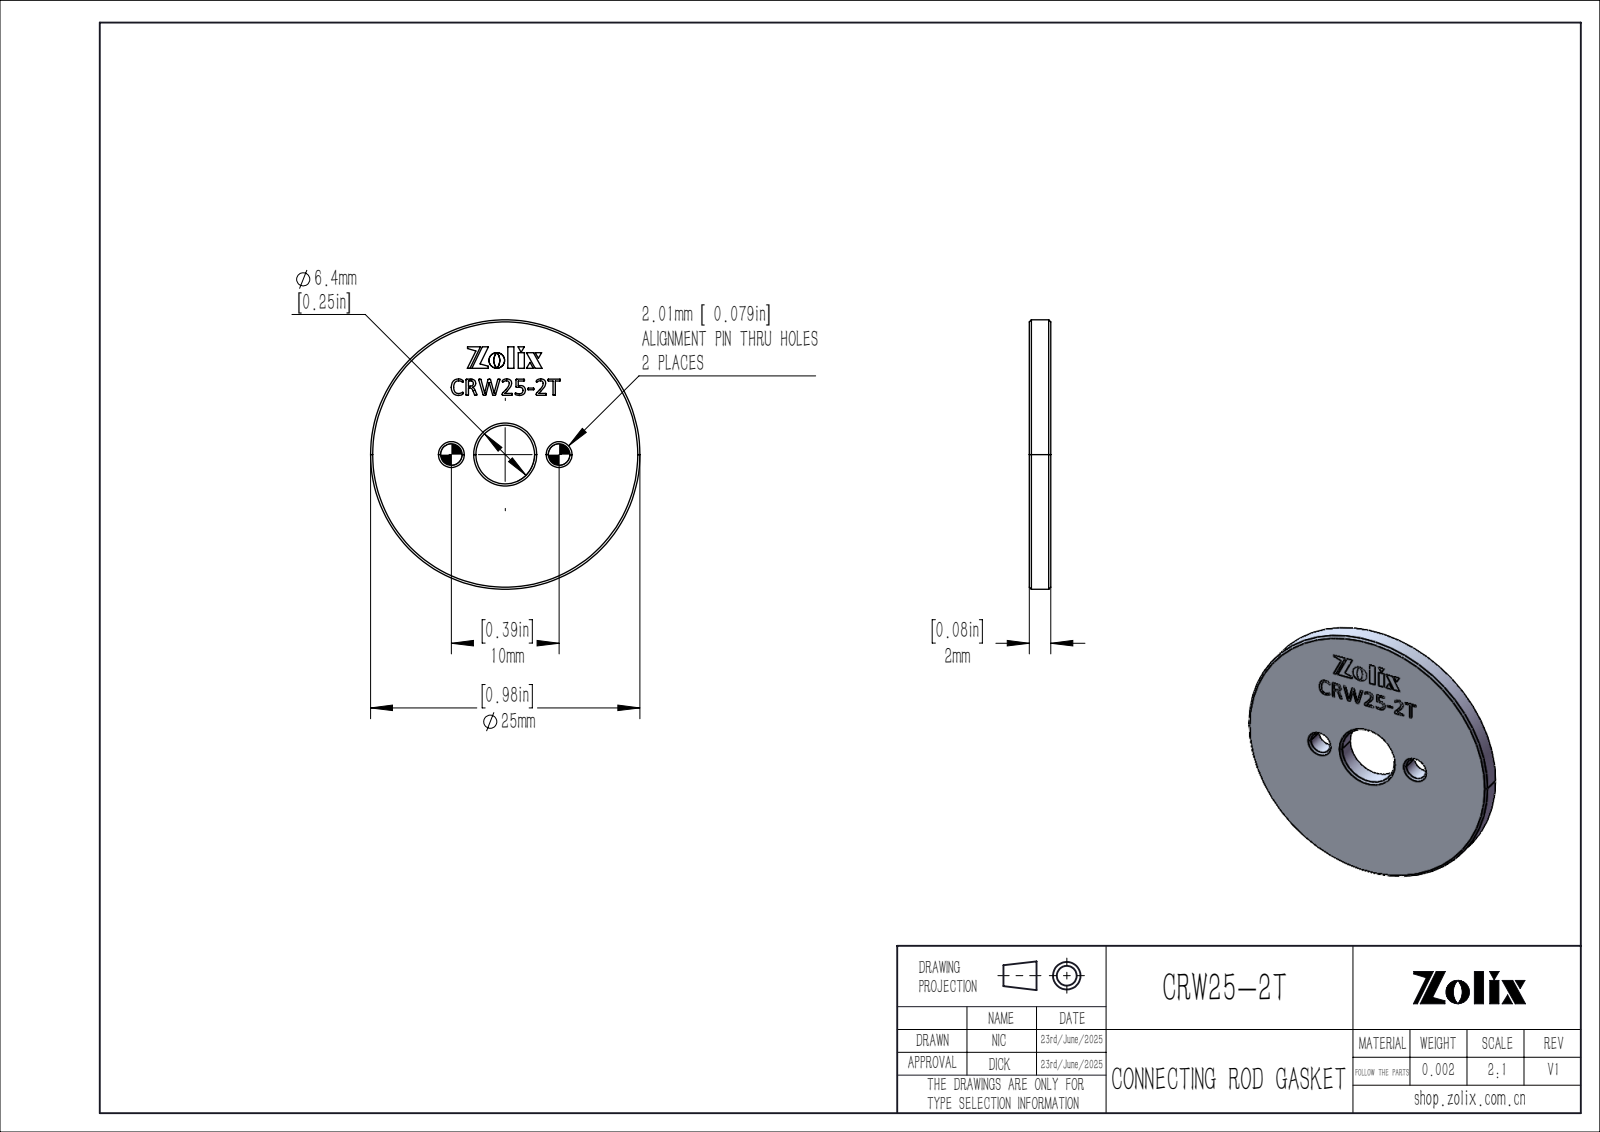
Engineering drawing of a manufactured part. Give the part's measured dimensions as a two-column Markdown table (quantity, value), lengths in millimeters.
| quantity | value |
| --- | --- |
| part name | CRW25-2T |
| STEP written by | SolidWorks 2020 (CONFIG_CONTROL_DESIGN) |
| units | millimeters |
| bodies | 1 solid, 326 faces (223 planar, 8 cylindrical, 95 other) |
| overall size | 25 × 25 × 2 |
| volume | 918 mm³ |
| surface area | 1 116 mm² |
| round holes (diameter × count) | 2 × 2, 5.45 × 1 |
| round bosses / shafts (diameter × count) | 25 × 1 |
| main face-to-face distances | 2, 1.98, 0.56, 1.32, 8.07, 1, 3, 0.96, 1.44, 2.44 |
| hole center spacings | 5, 10 |
